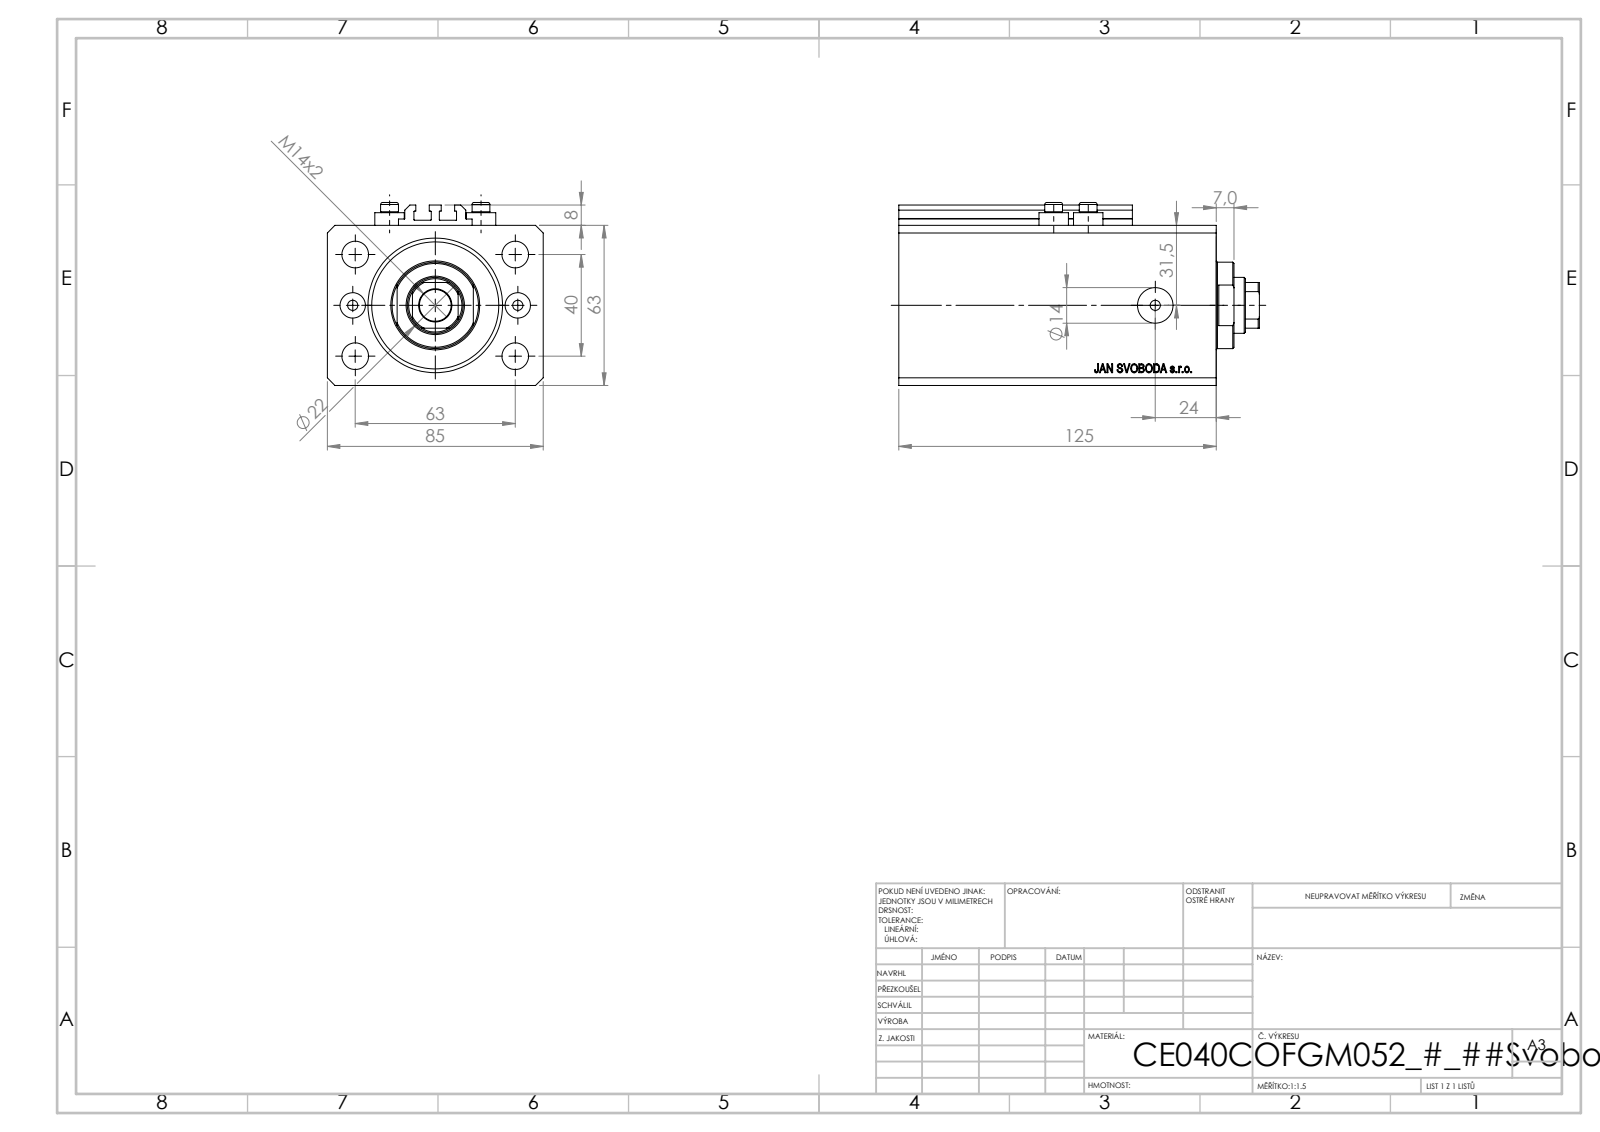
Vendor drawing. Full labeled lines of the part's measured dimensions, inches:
Part name (STEP PRODUCT): V250CE_C_Body; ALLEN BOLT V250CE; V250CE_C_VCP; V250CE_VC_C
STEP written by: SolidWorks 2019 (CONFIG_CONTROL_DESIGN)
Units: inches
Bodies: 8 solids, 1034 faces (504 planar, 86 cylindrical, 444 other)
Overall size (bounding box): 5.591 × 3.346 × 2.835
Volume: 36.36 in³ · Surface area: 178.4 in²
Round holes (diameter × count): ⌀0.157 ×8, ⌀0.413 ×4, ⌀0.394 ×2, ⌀0.551 ×2, ⌀0.492 ×1, ⌀0.866 ×1, ⌀1.575 ×1, ⌀2.087 ×1
Round bosses / shafts (diameter × count): ⌀0.457 ×4, ⌀0.276 ×4, ⌀1.339 ×1
Partial cylindrical surfaces — rounded edges, fillets, slot ends (radius × count): R0.008 ×10, R0.413 ×1
Main face-to-face distances: 2.48, 3.346, 4.921, 0.669, 4.252, 0.449, 3.803, 4.472, 0.098, 0.394
Hole centre spacings: 0.788, 1.469, 2.64, 0.535, 1.28, 1.417, 1.515, 1.575
